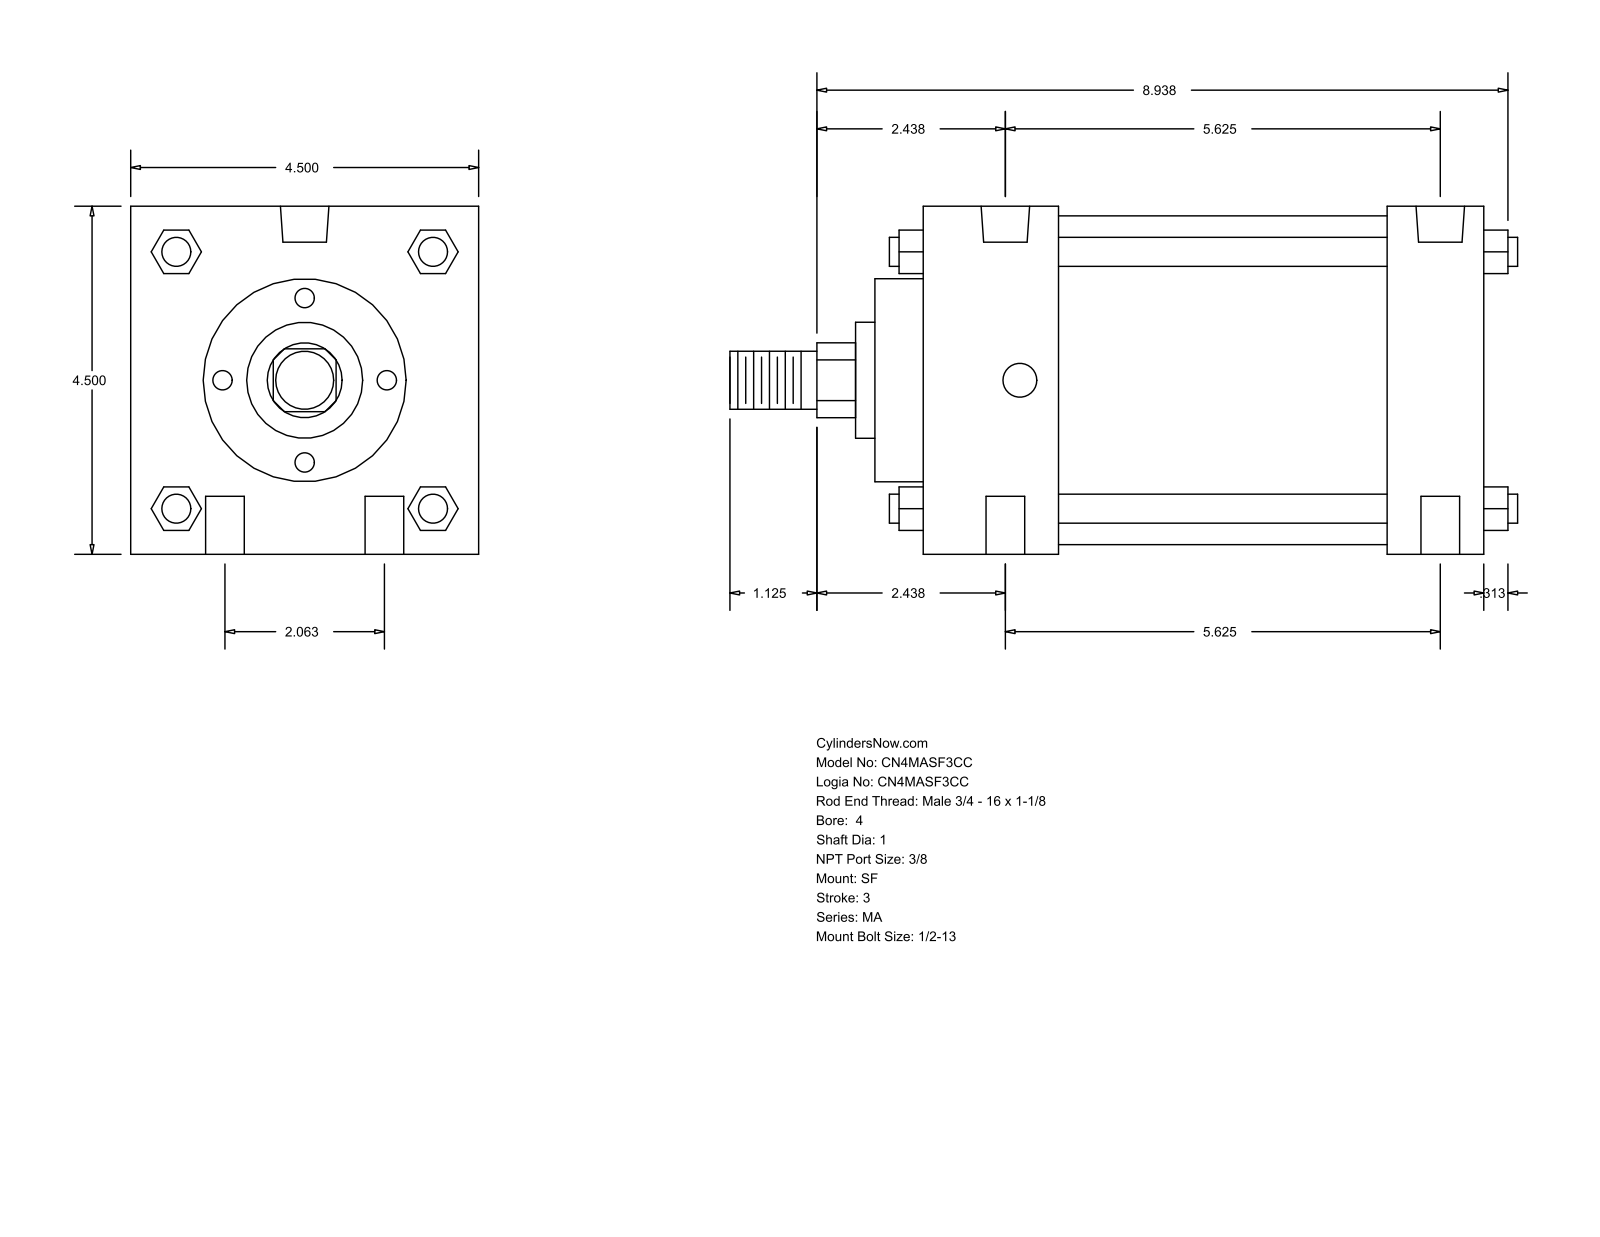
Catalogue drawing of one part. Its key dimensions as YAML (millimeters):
part_name: "MA_SF__0400_1"
step_written_by: "GSSL Pune (CONFIG_CONTROL_DESIGN)"
units: millimeters
bodies: {solids: 0, faces: 126, planar: 95, cylindrical: 31, other: 0}
overall_size: [258.76, 114.3, 114.3]
round_holes:
  - {diameter: 12.7, count: 4}
  - {diameter: 11.11, count: 2}
  - {diameter: 15.93, count: 2}
round_bosses_or_shafts:
  - {diameter: 9.53, count: 4}
  - {diameter: 107.95, count: 1}
  - {diameter: 66.67, count: 1}
  - {diameter: 38.1, count: 1}
  - {diameter: 25.4, count: 1}
  - {diameter: 19.05, count: 1}
partial_cylinders:
  - {radius: 12.29, count: 1}
face_to_face_distances: [114.3, 184.15, 152.4, 31.75, 44.46, 107.94, 139.69, 200.02, 15.87, 60.33]
hole_center_spacings: [26.19, 145.26, 142.88, 52.38, 152.18, 133.36]
